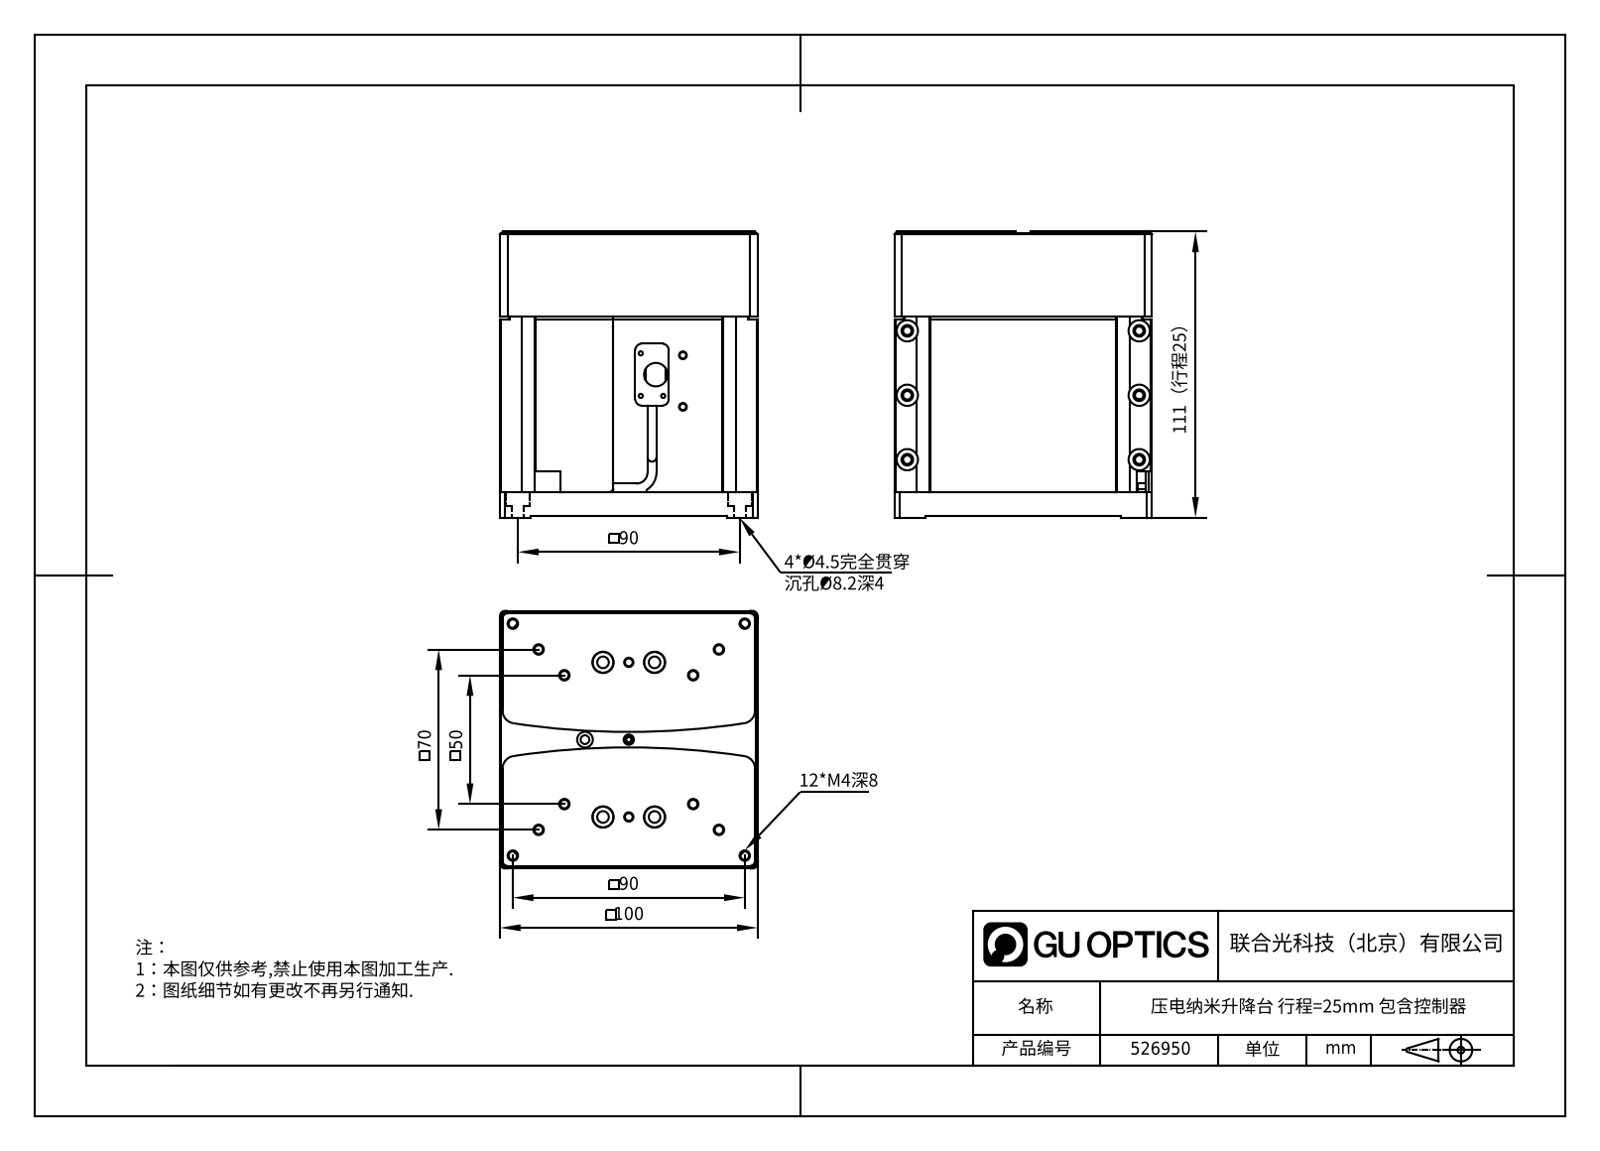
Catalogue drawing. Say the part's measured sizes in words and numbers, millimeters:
The part is named "526950". Its 3-D file was written by "SolidWorks 2020 (CONFIG_CONTROL_DESIGN)". It is 0 solids with 1181 faces: 683 planar, 290 cylindrical and 208 other. Overall it measures 111 by 100 by 100 millimeters. Round holes: 23 of diameter 3.3, 22 of diameter 4.5, 13 of diameter 8, 12 of diameter 2.5, 10 of diameter 3, 10 of diameter 8.25, 7 of diameter 6.1, 6 of diameter 6.5, 4 of diameter 5.5, 4 of diameter 6.2, 4 of diameter 8.2, 4 of diameter 10. Round bosses or shafts: 1 of diameter 8.95, 1 of diameter 3.5, 1 of diameter 0.51. Partial cylindrical surfaces (rounded edges, fillets, slot ends): 20 of radius 0.2, 14 of radius 5, 12 of radius 2, 12 of radius 3, 12 of radius 3.5, 8 of radius 0.8, 8 of radius 2.5, 6 of radius 0.55. The main face-to-face distances are 100, 93.5, 6.5, 10, 0.5, 44, 7.5, 3.5, 110.5, 3. The hole center spacings are 11.18, 30, 40, 40.31, 90, 14.14, 25, 5.
